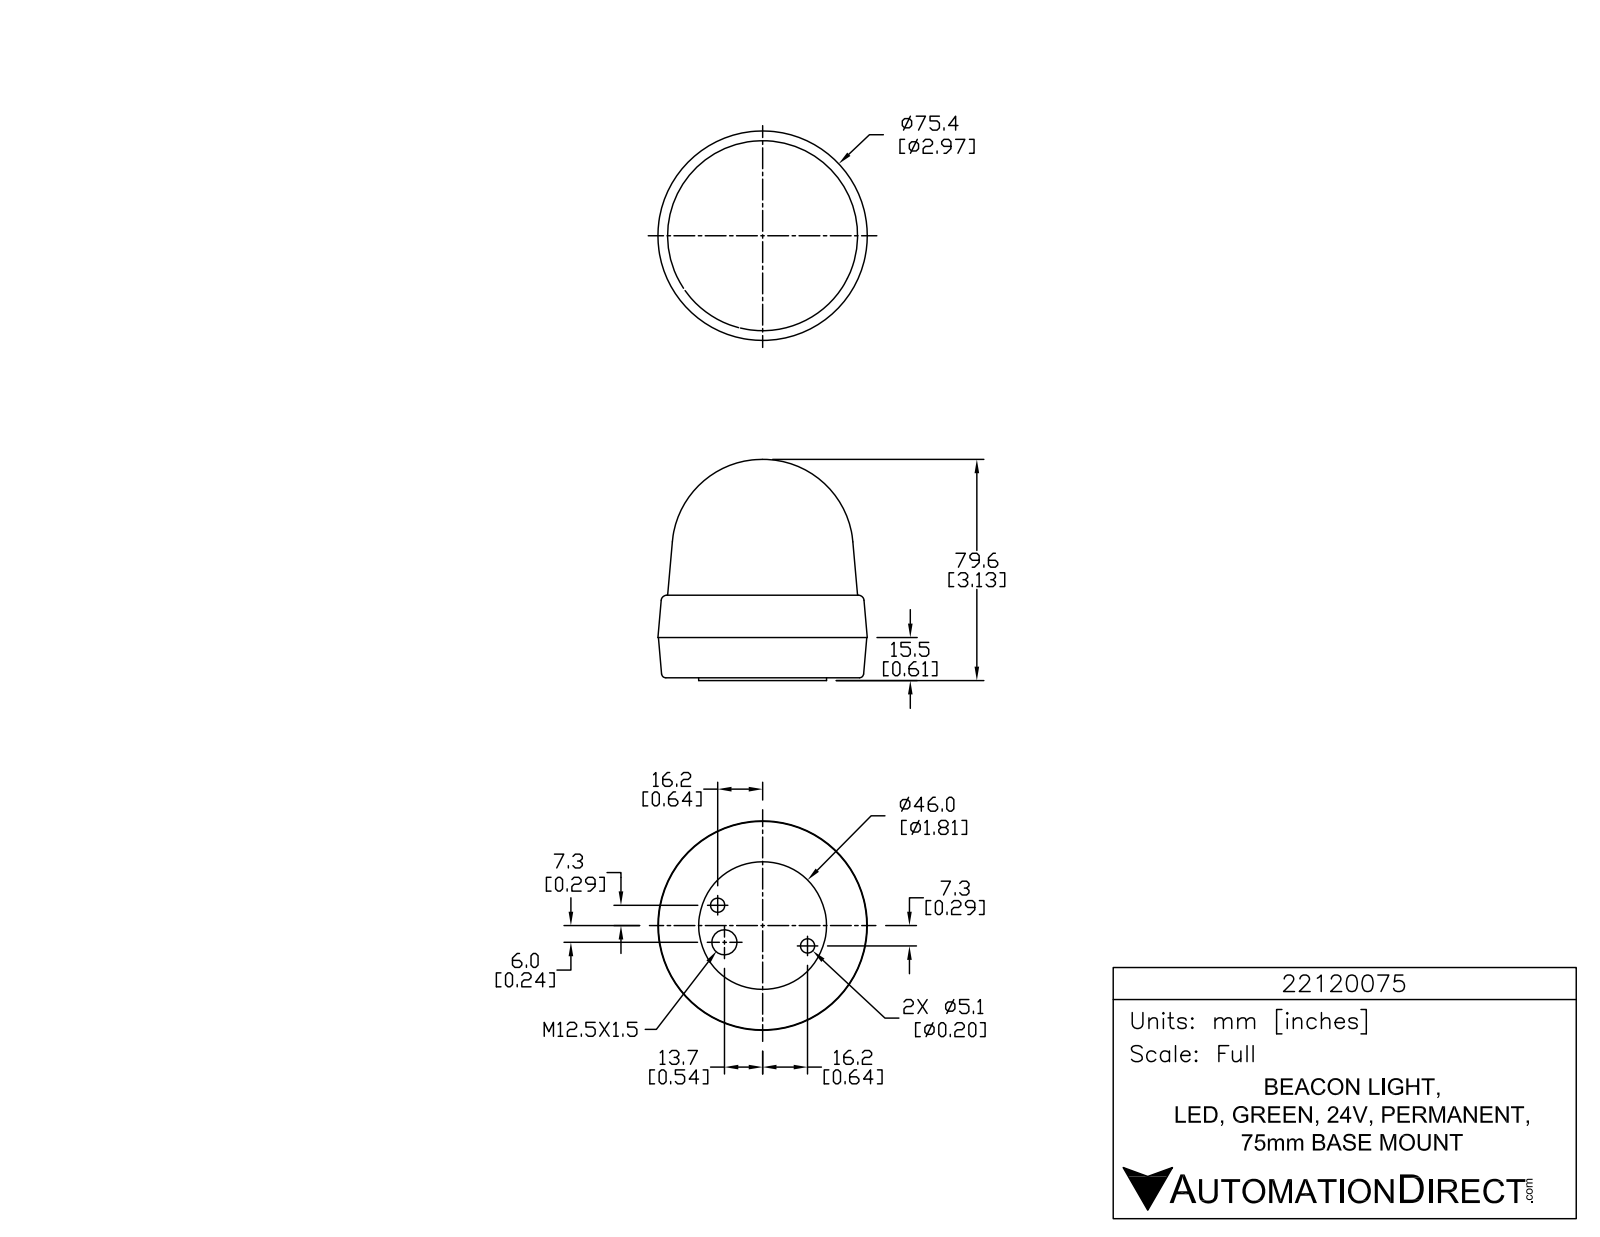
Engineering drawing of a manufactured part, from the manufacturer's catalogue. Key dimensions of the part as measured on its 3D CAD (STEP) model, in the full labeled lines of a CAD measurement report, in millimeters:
Part name (STEP PRODUCT): 22120075
STEP written by: SolidWorks 2015 (AUTOMOTIVE_DESIGN)
Units: millimetres
Bodies: 1 solid, 773 faces (526 planar, 163 cylindrical, 84 other)
Overall size (bounding box): 79.6 × 75.4 × 75.4
Volume: 258 800 mm³ · Surface area: 21 740 mm²
Round holes (diameter × count): ⌀1.5 ×3, ⌀5.1 ×2, ⌀9 ×1
Round bosses / shafts (diameter × count): ⌀8.6 ×3, ⌀2.1 ×3, ⌀46 ×1
Partial cylindrical surfaces — rounded edges, fillets, slot ends (radius × count): R0.1 ×9, R0.1 ×6, R0.3 ×6, R0.3 ×6, R0.3 ×6, R5 ×6, R0.1 ×3, R0.1 ×3
Main face-to-face distances: 1, 30.7, 29.7, 15.5, 14.5, 15.2, 39.8, 38.8, 24.3, 9.1
Hole centre spacings: 13.6, 29.9, 35.5
